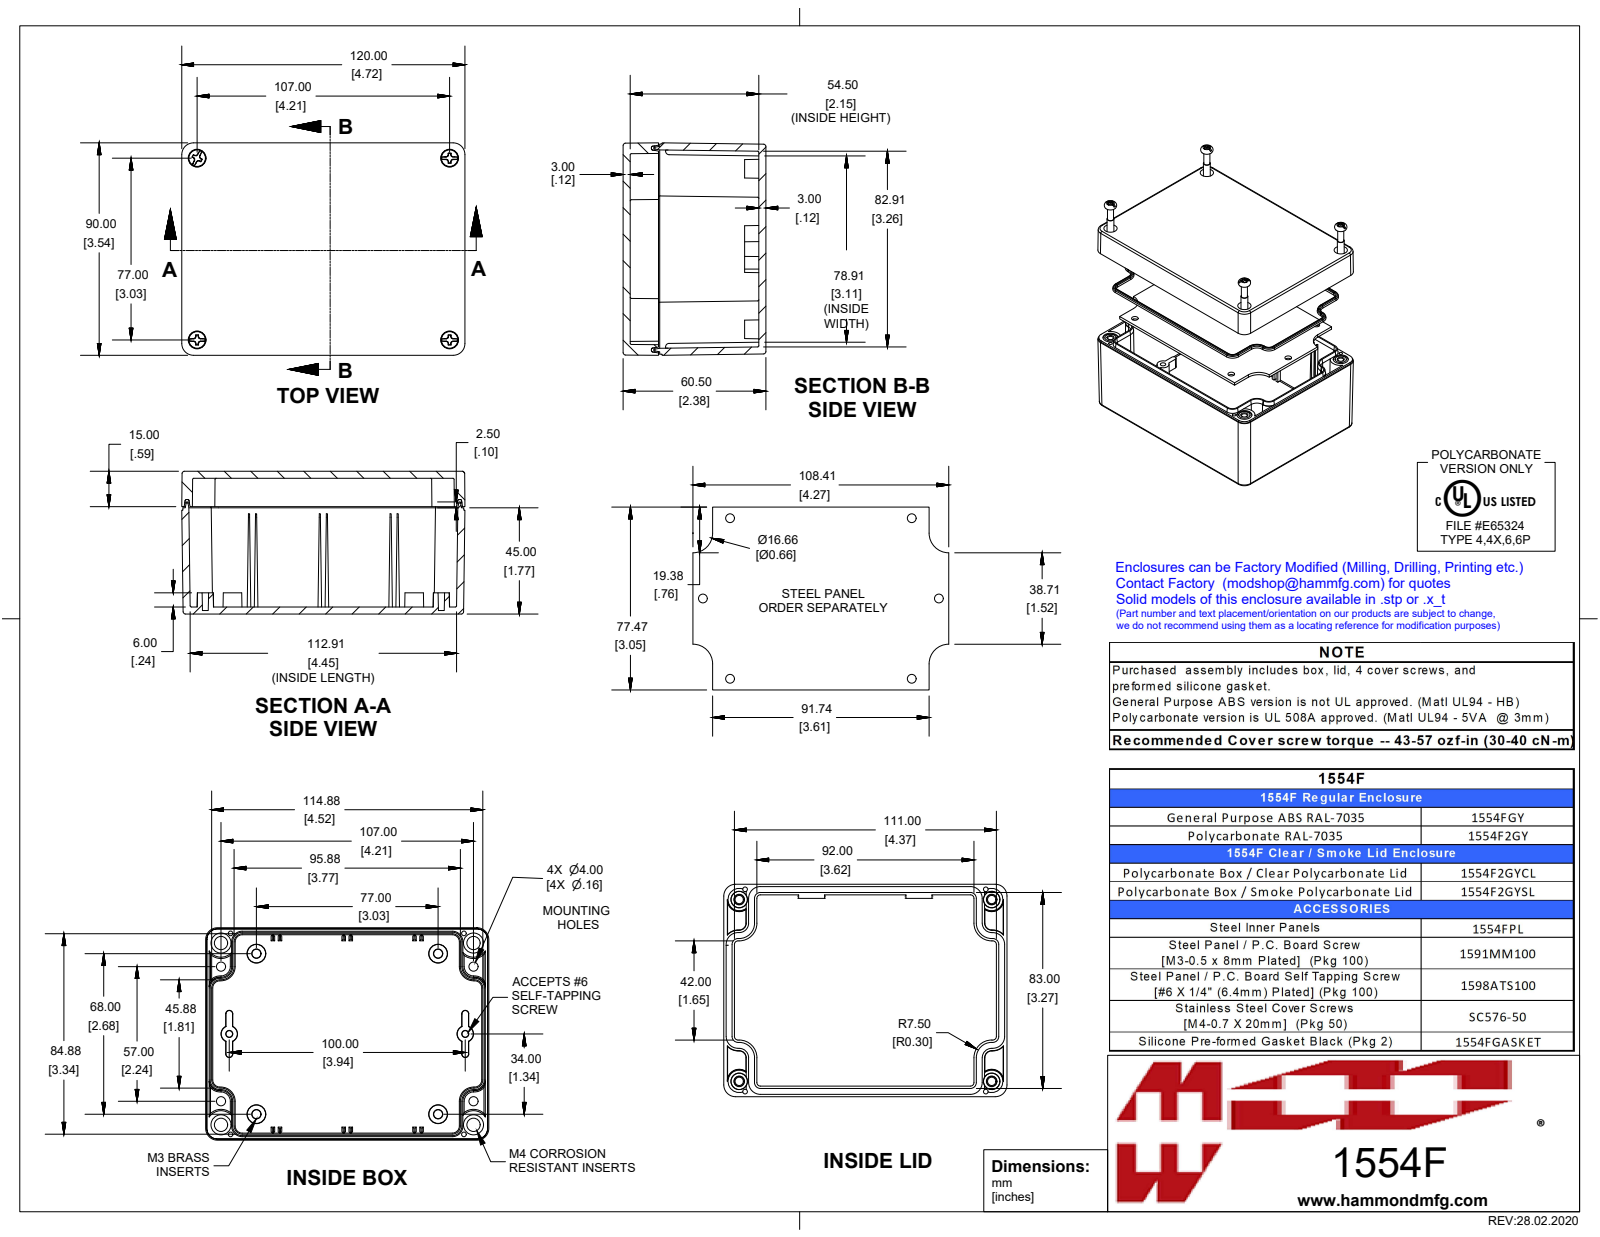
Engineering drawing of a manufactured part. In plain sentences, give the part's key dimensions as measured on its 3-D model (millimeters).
The part is named "1554FGY". Its 3-D file was written by "SolidWorks 2019 (AUTOMOTIVE_DESIGN)". It is 15 solids with 1384 faces: 402 planar, 352 cylindrical and 630 other. Overall it measures 120 by 90 by 60.5 millimeters. Its volume is 152 600 cubic millimeters and its surface area 113 100 square millimeters. Round holes: 8 of diameter 2, 4 of diameter 2.5, 4 of diameter 3.3, 4 of diameter 3.5, 4 of diameter 7, 4 of diameter 8.5. Round bosses or shafts: 4 of diameter 6.4, 4 of diameter 5.5, 4 of diameter 5.3, 4 of diameter 4.8, 4 of diameter 3.9, 4 of diameter 3.9, 4 of diameter 3.8, 4 of diameter 3.4. Partial cylindrical surfaces (rounded edges, fillets, slot ends): 36 of radius 0.5, 8 of radius 1, 8 of radius 5, 4 of radius 4.7, 3 of radius 1.5. The main face-to-face distances are 3, 57.5, 60.5, 54.5, 1.5, 12.5, 4.5, 9.5, 11, 2. The hole center spacings are 5, 15.3, 15.7, 74, 77, 77.9, 81.4, 89.9.
